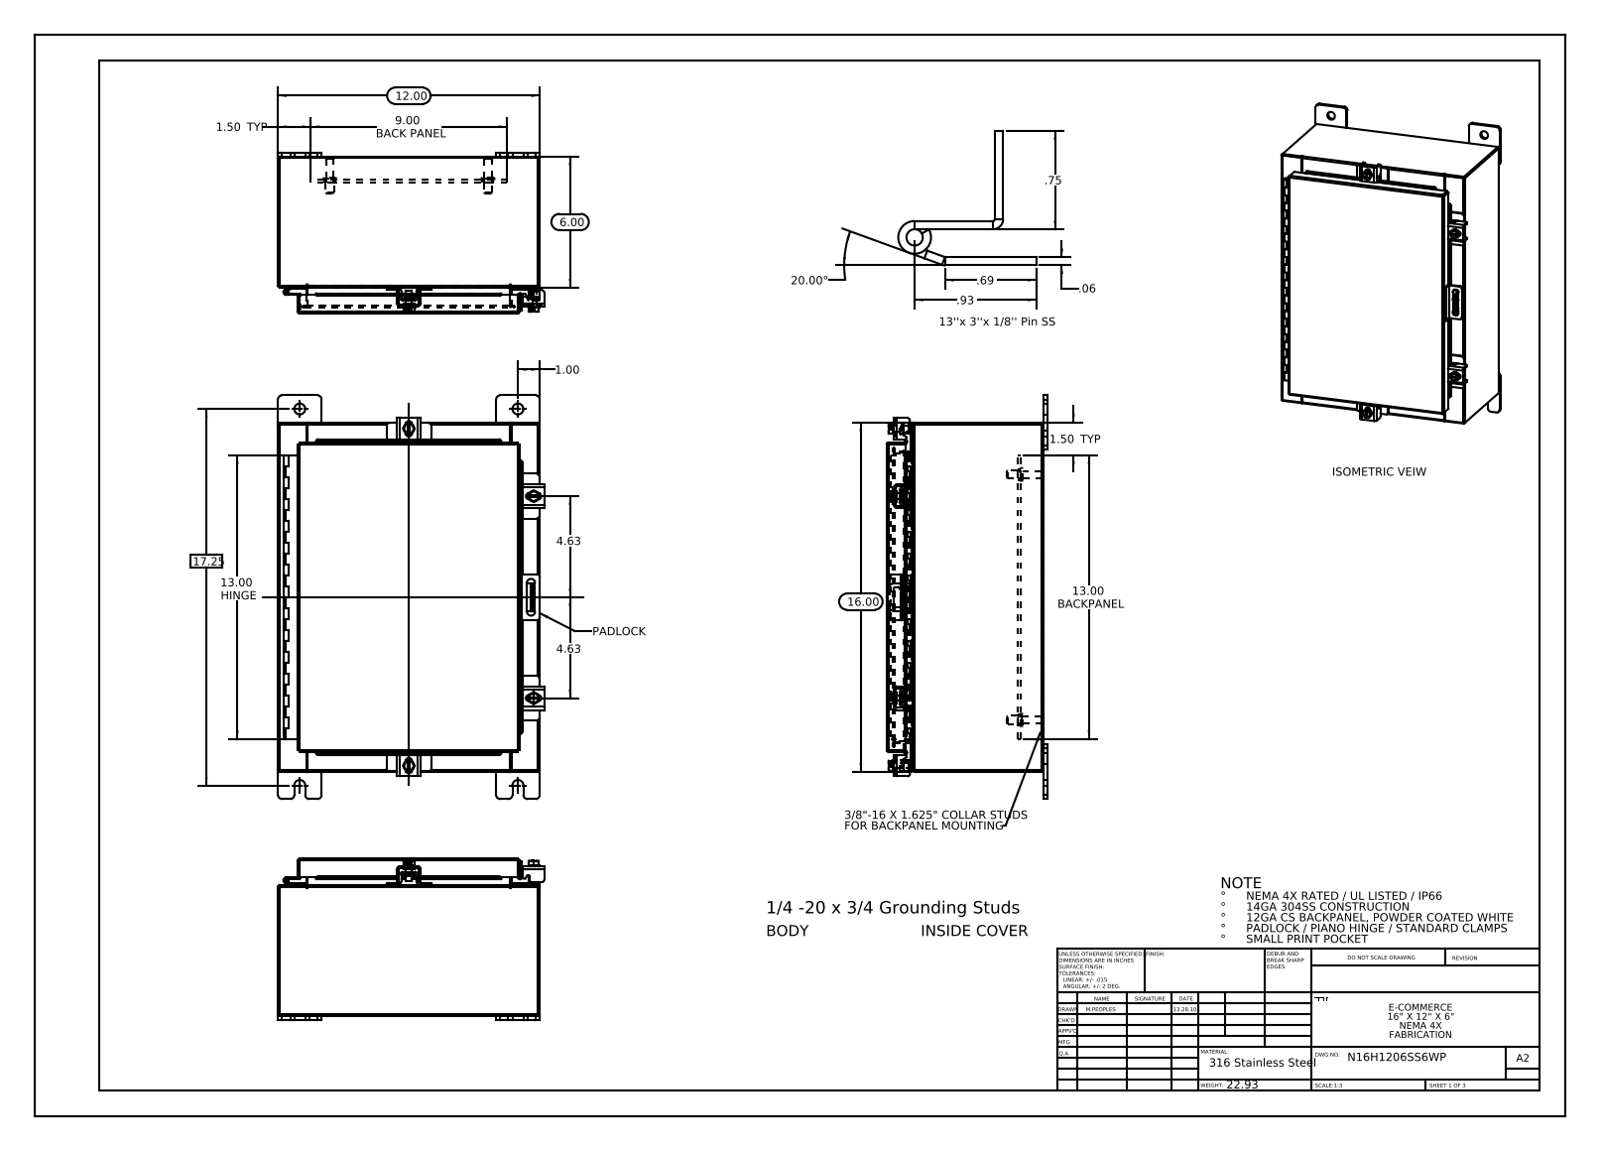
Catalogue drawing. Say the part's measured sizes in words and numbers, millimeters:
The part is named "N16H1206SS6WP Body; N16H1206SS6WP Padlock Hasp; N16H1206SS6WP Backpanel; N16H1206SS6WP Padlock Staple (+8 more)". Its 3-D file was written by "SolidWorks 2013 (CONFIG_CONTROL_DESIGN)". It is 37 solids with 1267 faces: 680 planar, 507 cylindrical and 80 other. Overall it measures 469.9 by 310.2 by 187.7 millimeters. Its volume is 1 333 000 cubic millimeters and its surface area 1 337 000 square millimeters. Round holes: 8 of diameter 12.7, 4 of diameter 5.4, 4 of diameter 6.6, 2 of diameter 3.2, 1 of diameter 3.2. Round bosses or shafts: 5 of diameter 6.4, 4 of diameter 15.9, 4 of diameter 12.7, 4 of diameter 10.1, 4 of diameter 9.5, 4 of diameter 8.4. Partial cylindrical surfaces (rounded edges, fillets, slot ends): 24 of radius 4.8, 23 of radius 0.3, 22 of radius 1.5, 21 of radius 2.2, 10 of radius 3.2, 8 of radius 3, 8 of radius 3.6, 7 of radius 1.3. The main face-to-face distances are 1.9, 181, 302.9, 182.9, 179.1, 404.5, 150.5, 30.5, 25.4, 27.3. The hole center spacings are 351.4, 56.5, 59.1, 83.8, 106.4, 106.4, 127.3, 129.
